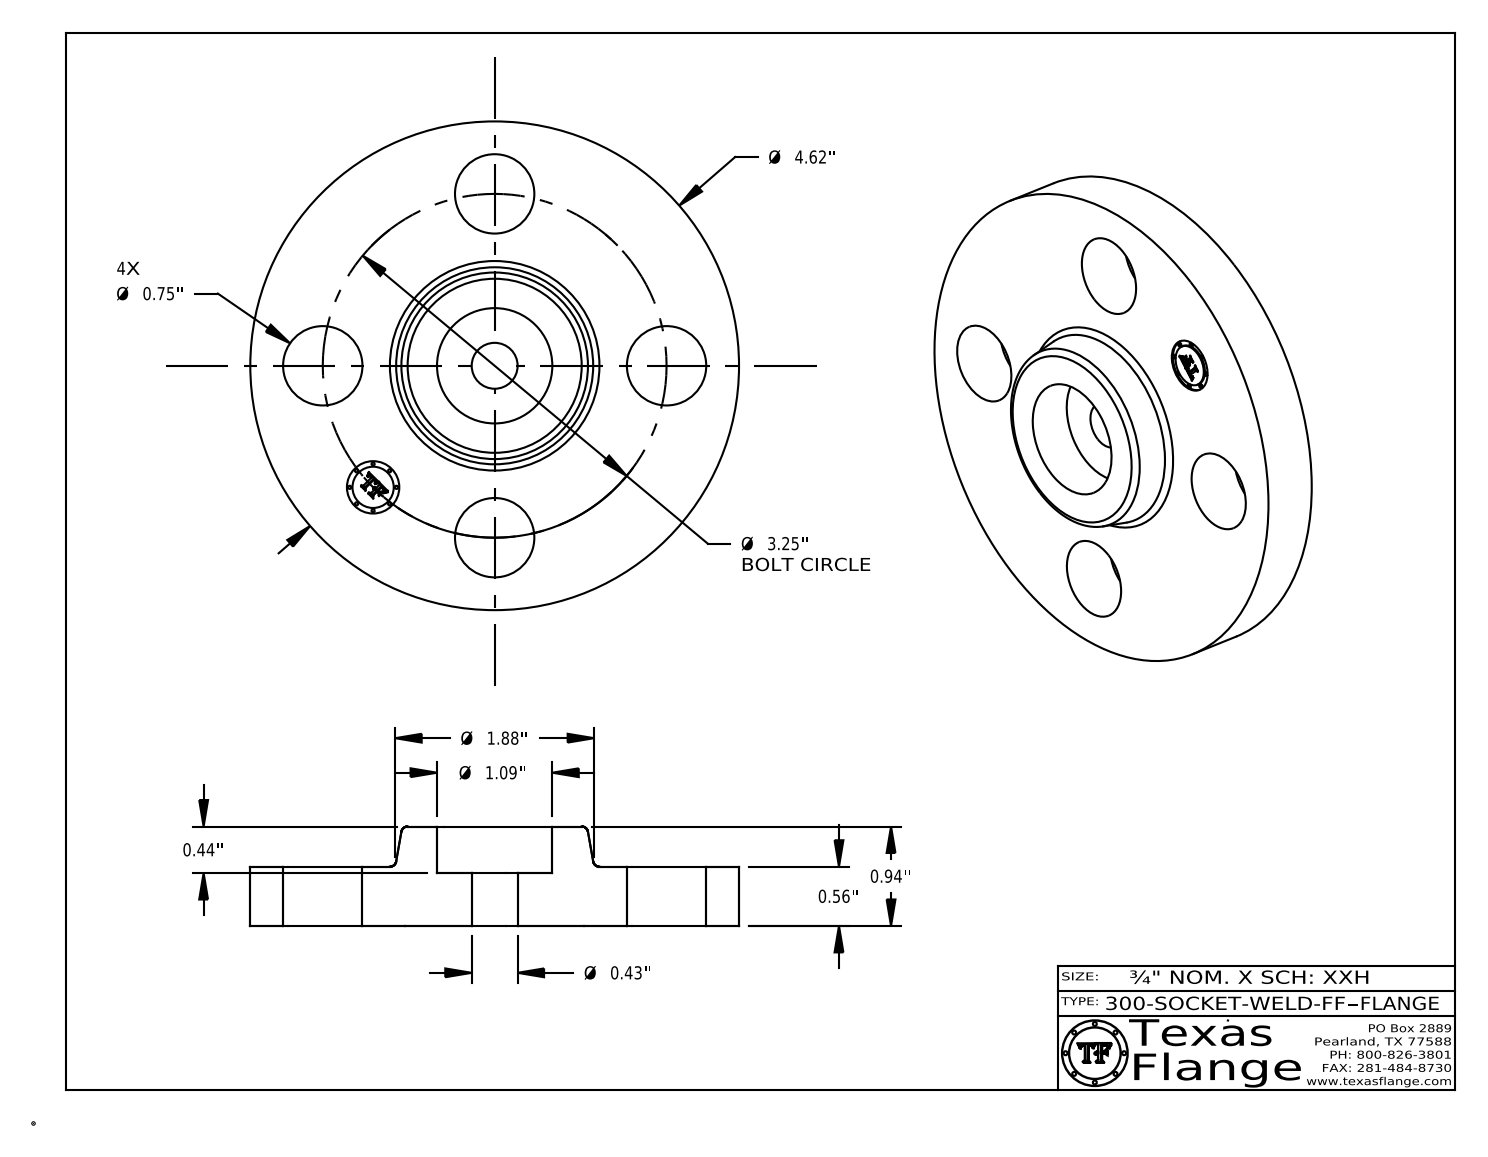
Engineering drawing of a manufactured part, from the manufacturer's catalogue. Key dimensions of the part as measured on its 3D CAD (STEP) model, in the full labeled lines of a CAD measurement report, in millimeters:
Part name (STEP PRODUCT): 300-SOCKET-WELD-FF
STEP written by: CATIA V5 STEP AP214 (AUTOMOTIVE_DESIGN)
Units: millimetres
Bodies: 1 solid, 410 faces (370 planar, 34 cylindrical, 6 other)
Overall size (bounding box): 117.3 × 117.3 × 23.9
Volume: 145 700 mm³ · Surface area: 30 330 mm²
Round holes (diameter × count): ⌀19.1 ×4, ⌀11 ×1, ⌀12.6 ×1, ⌀27.7 ×1
Round bosses / shafts (diameter × count): ⌀0.8 ×8, ⌀117.3 ×1, ⌀9.9 ×1
Main face-to-face distances: 14.2, 23.9, 9.7, 12.7, 1.5, 11.2, 13.8, 1.1, 0.4, 10
Hole centre spacings: 41.3, 58.4, 31.6, 76.3, 82.6
